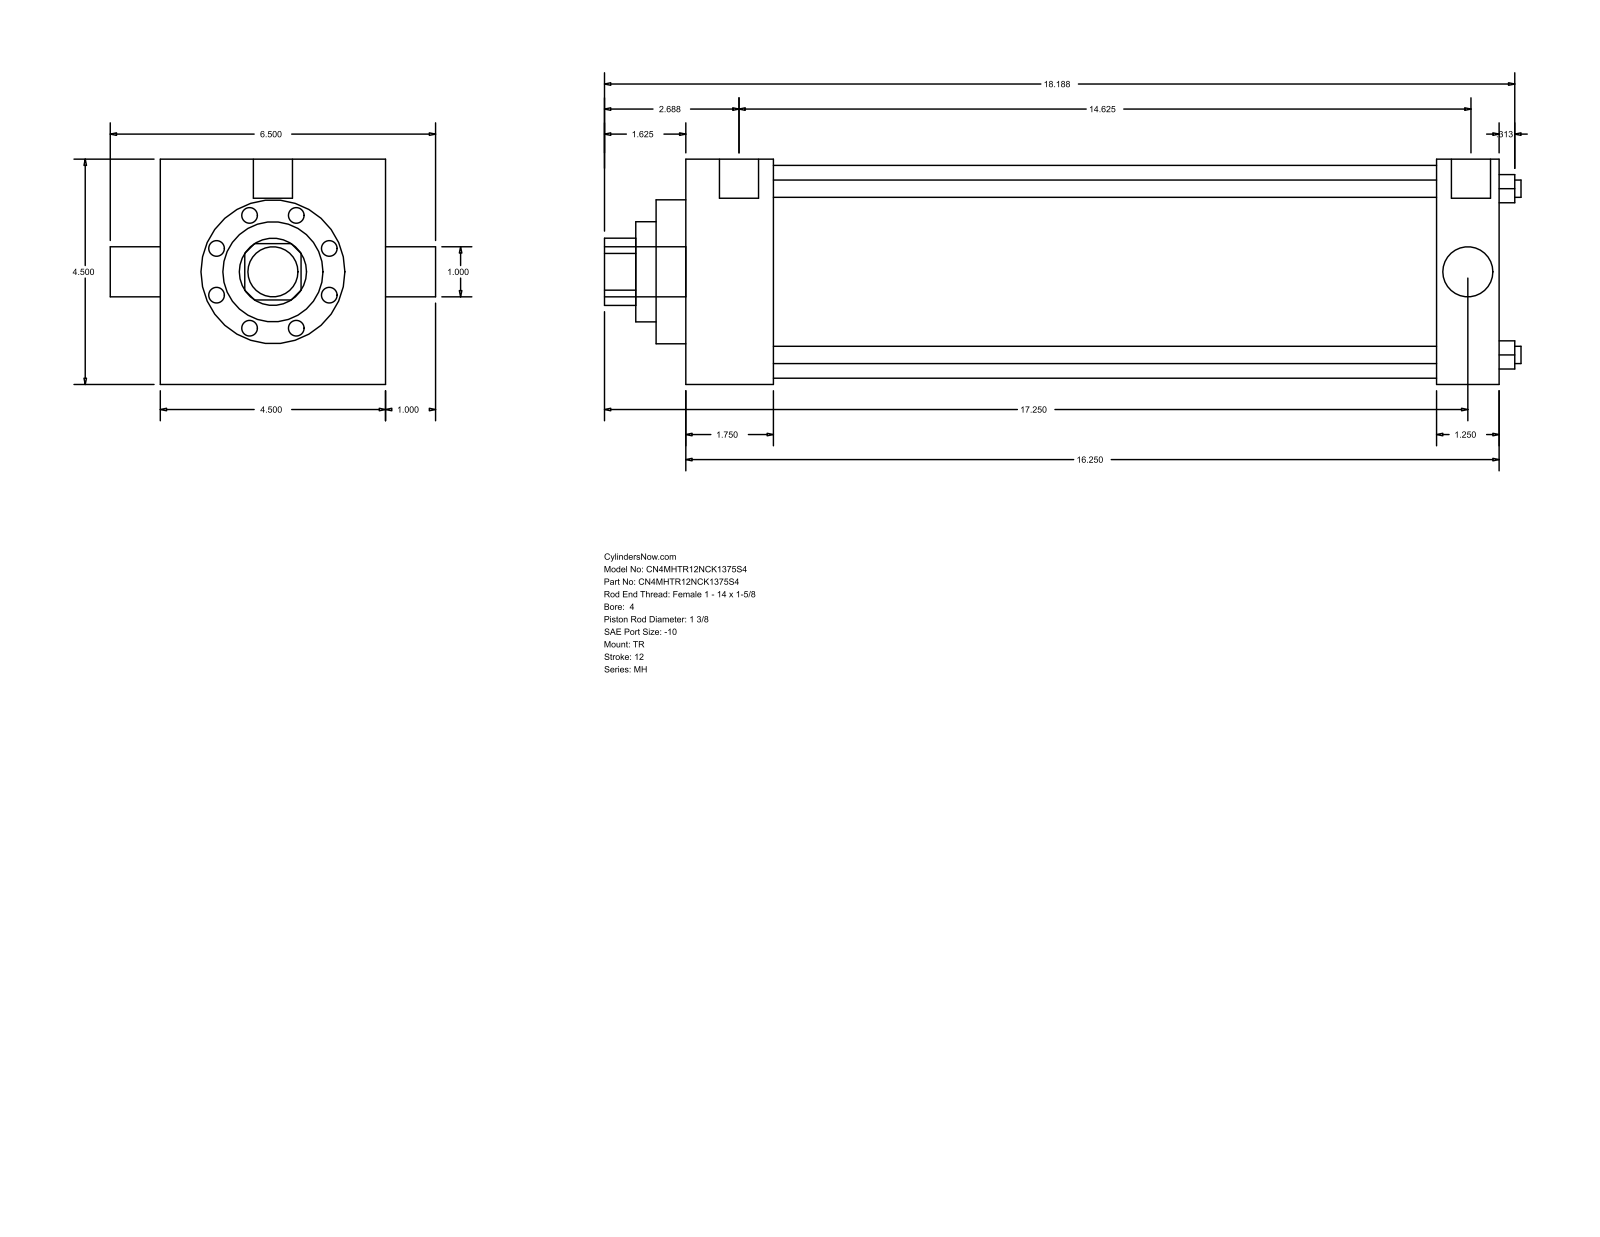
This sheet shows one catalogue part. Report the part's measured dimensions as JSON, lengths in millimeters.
{"part_name": "MH_TR__0400_1.375", "step_written_by": "GSSL Pune (CONFIG_CONTROL_DESIGN)", "units": "millimeters", "bodies": {"solids": 0, "faces": 86, "planar": 61, "cylindrical": 25, "other": 0}, "overall_size": [465.14, 165.1, 114.3], "round_holes": [[8.76, 4], [25.4, 1], [34.92, 1], [50.8, 1], [73.03, 1], [107.95, 1]], "round_bosses_or_shafts": [[8.73, 3], [19.84, 2], [25.4, 1]], "partial_cylinders_radius": [[17.06, 1]], "face_to_face_distances": [114.3, 412.75, 44.45, 368.3, 381, 336.55, 31.75, 15.08, 59.53, 396.08], "hole_center_spacings": [59.62, 84.32, 119.25]}
